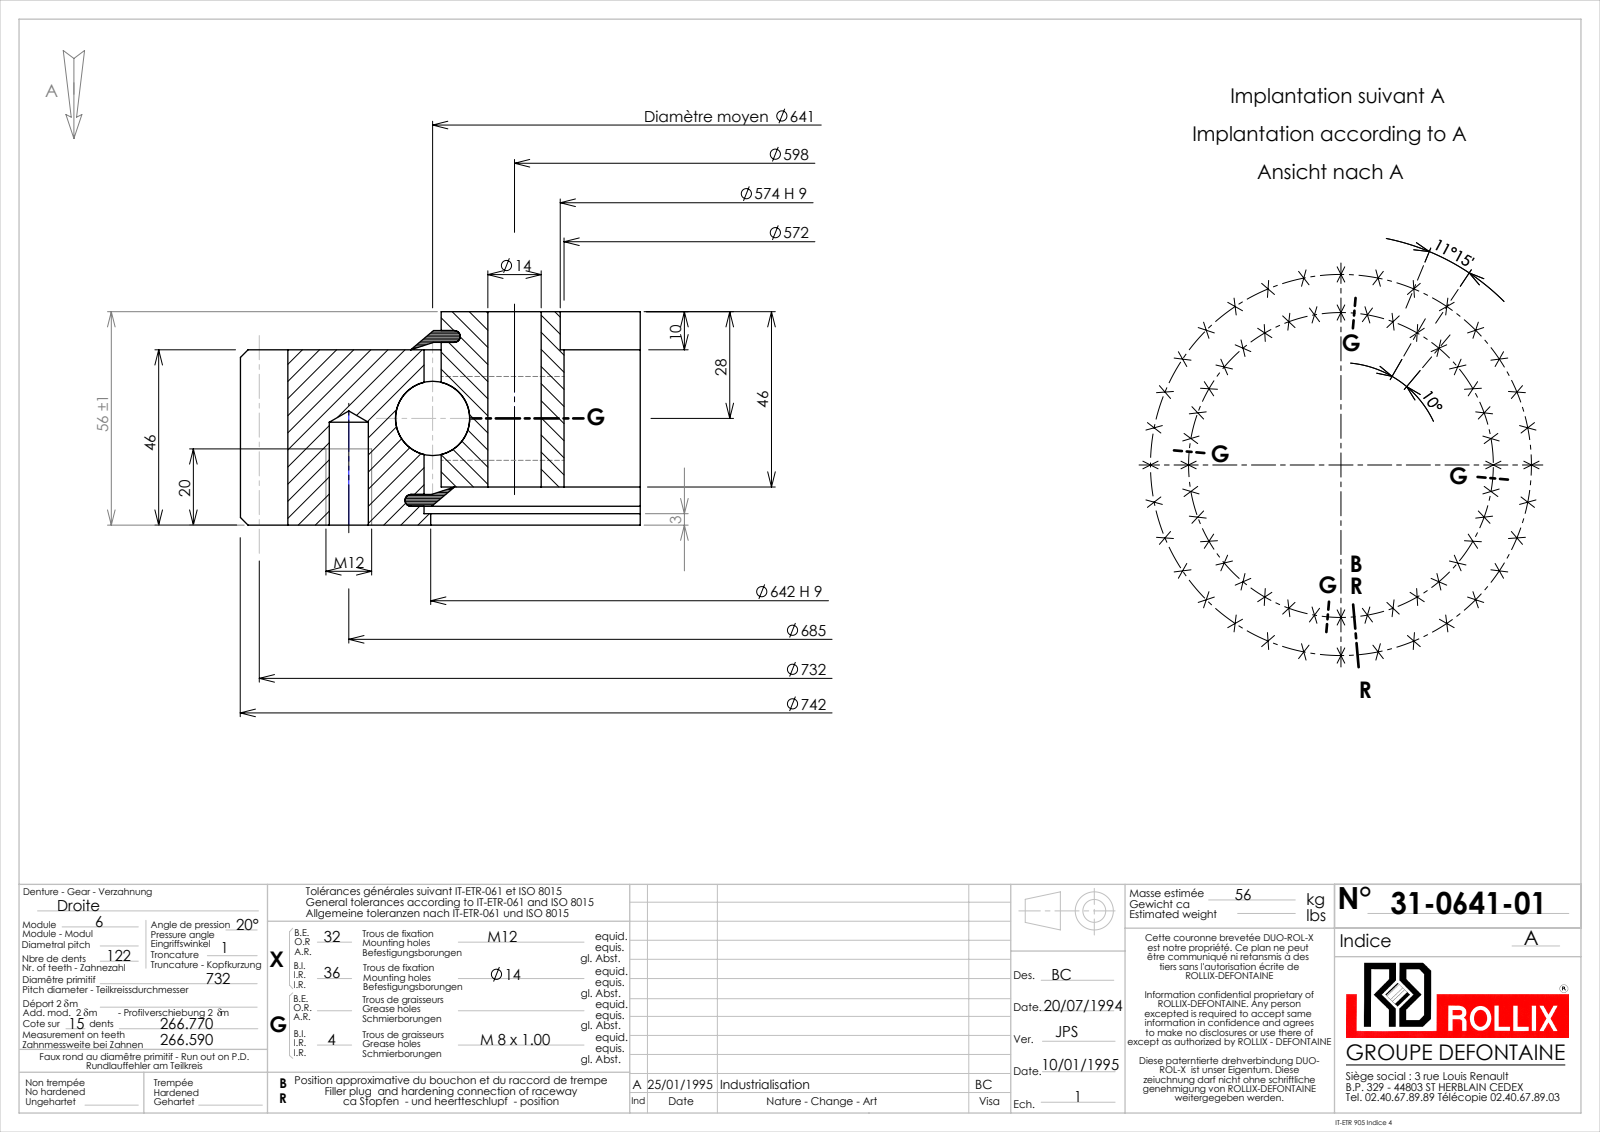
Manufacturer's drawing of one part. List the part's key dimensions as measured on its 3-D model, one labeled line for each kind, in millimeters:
Part name (STEP PRODUCT): 31-0641-01
STEP written by: SolidWorks 2016 (CONFIG_CONTROL_DESIGN)
Units: millimetres
Bodies: 9 solids, 1089 faces (298 planar, 415 cylindrical, 376 other)
Overall size (bounding box): 742 × 741.88 × 56
Volume: 6 355 000 mm³ · Surface area: 1 063 000 mm²
Round holes (diameter × count): ⌀14 ×36, ⌀10.25 ×32, ⌀7 ×4, ⌀572 ×1, ⌀574 ×1, ⌀642 ×1, ⌀645.5 ×1
Round bosses / shafts (diameter × count): ⌀8 ×4, ⌀636.5 ×1
Partial cylindrical surfaces — rounded edges, fillets, slot ends (radius × count): R358.5 ×1, R371 ×1
Main face-to-face distances: 46, 10, 36, 56, 5.05, 1.95, 43, 4.95, 51.05, 41.05
Hole centre spacings: 67.14, 262.14, 529.51, 681.7, 484.37, 632.86, 133.64, 655.5
